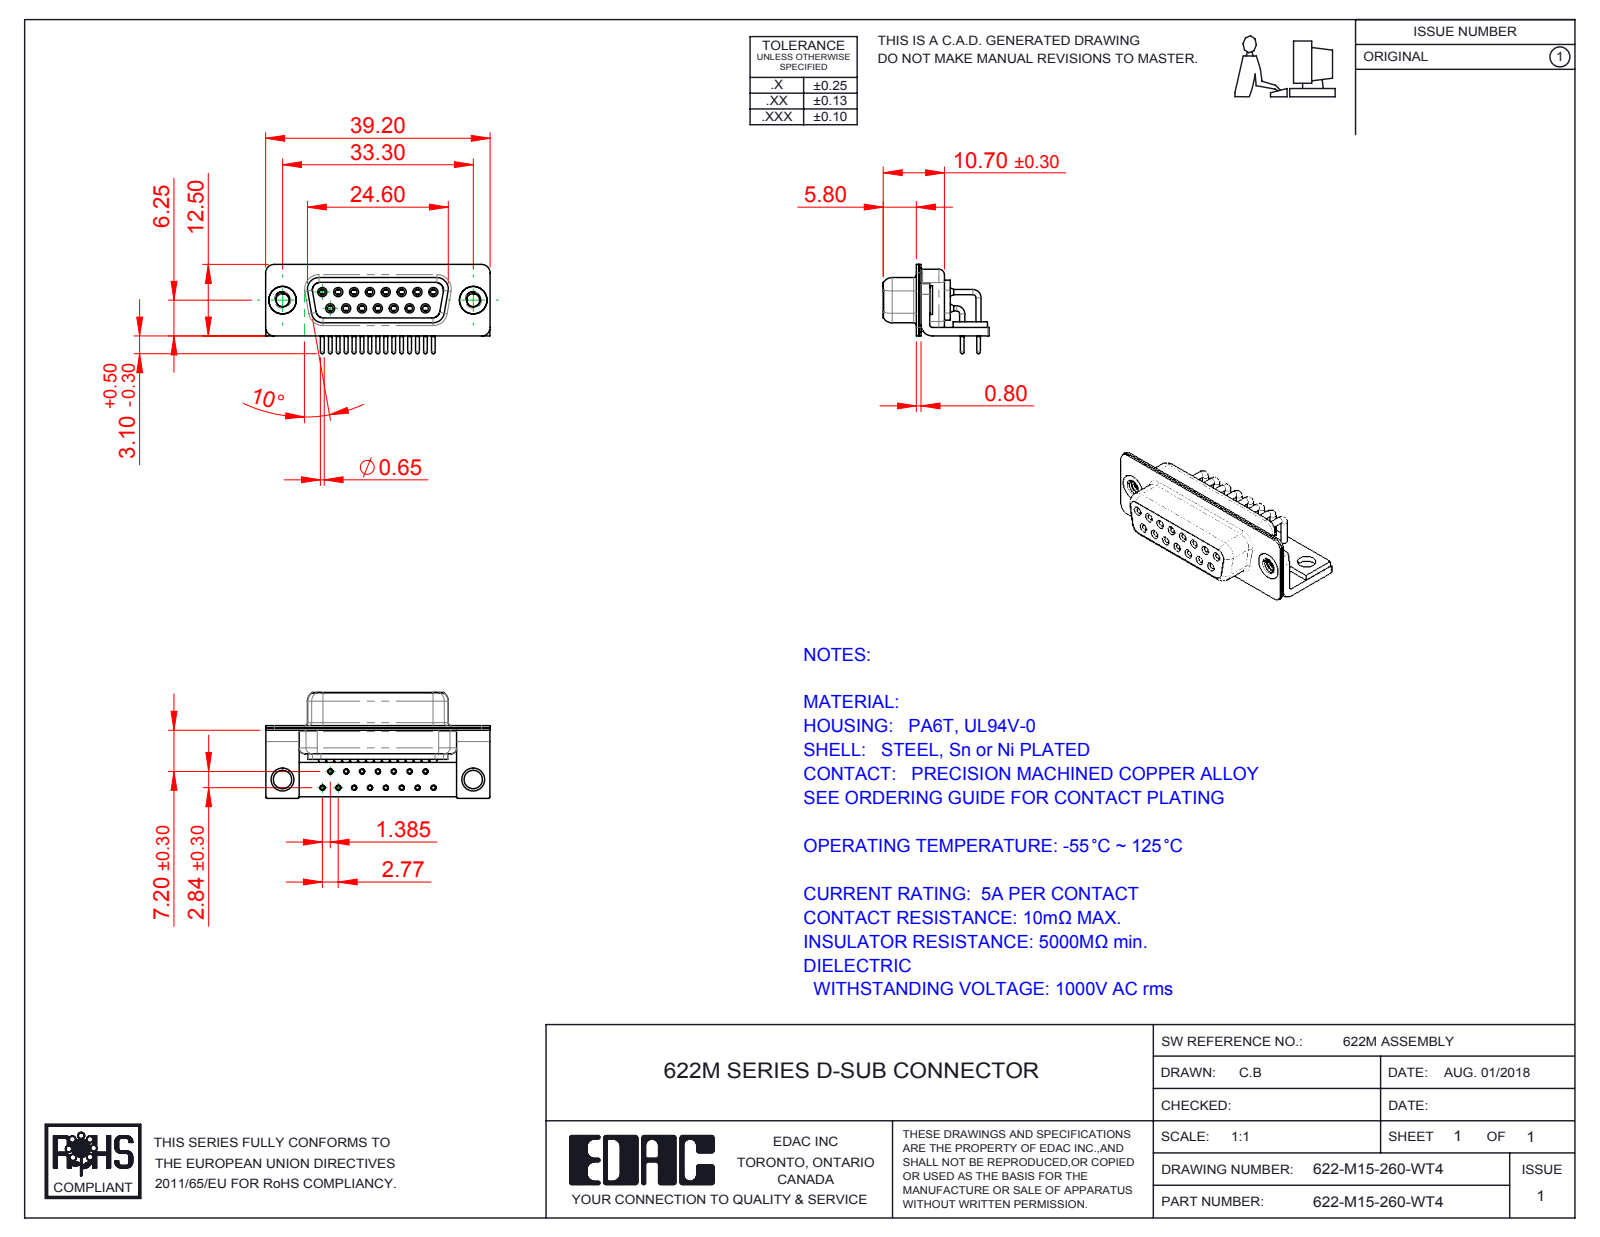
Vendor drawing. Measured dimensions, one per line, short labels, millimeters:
name: 622-M15-260-WT4; 622M Stabilizer Board_15 Contacts; 622M Stabilizer Bracket; 622M 4-40 Threaded Rivet_Stabilizer (+5 more)
written by: SolidWorks 2016 (CONFIG_CONTROL_DESIGN)
unit: mm
bodies: 23 solids, 1154 faces (318 planar, 534 cylindrical, 302 other)
size: 39.2 × 18.5 × 15.6
volume: 2 973 mm³; area: 7 506 mm²
holes: 15× ⌀0.9, 15× ⌀1, 15× ⌀1.1, 15× ⌀1.7, 15× ⌀1.8, 15× ⌀2, 2× ⌀2.26, 2× ⌀3.2, 2× ⌀4, 2× ⌀4.8
bosses: 22× ⌀0.9, 15× ⌀1.6, 15× ⌀1.5, 15× ⌀0.65, 2× ⌀5, 2× ⌀4.9
rounds: 16× R0.25, 16× R1.5, 13× R2, 8× R1.35, 8× R1.6, 5× R0.5, 4× R0.6, 4× R0.65
face distances: 0.4, 0.8, 2.3, 1.9, 9.35, 1, 1.5, 1.45, 8.95, 0.85
hole spacings: 3.16, 2.77, 5.54, 8.31, 11.08, 5.03, 5.04, 7.48
